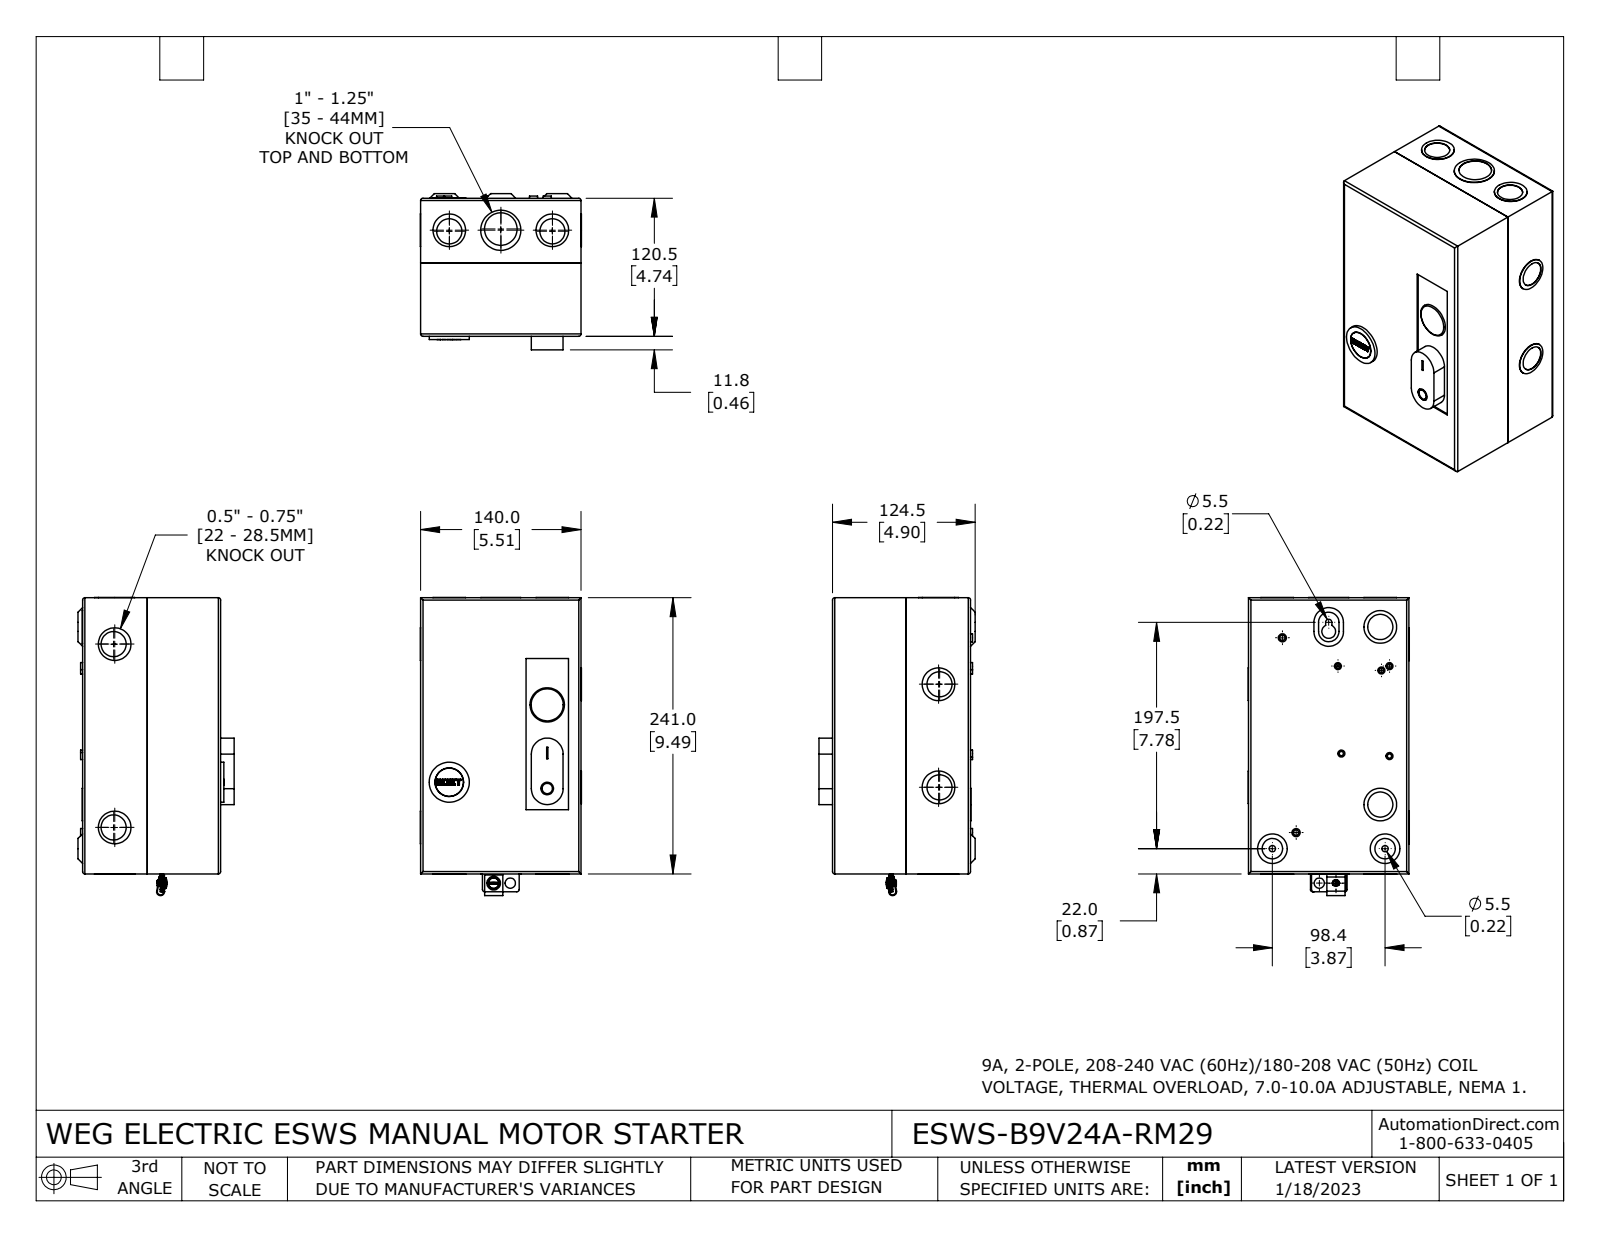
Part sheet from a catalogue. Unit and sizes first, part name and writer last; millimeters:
Units: millimetres
Overall size (bounding box): 260.3 × 140.6 × 136.3
Round holes (diameter × count): ⌀3.7 ×5, ⌀21.9 ×4, ⌀4.6 ×2, ⌀5.5 ×2, ⌀9 ×2, ⌀21.9 ×2, ⌀22 ×2, ⌀22.5 ×2, ⌀6.5 ×1, ⌀7.7 ×1, ⌀11 ×1, ⌀11.9 ×1
Round bosses / shafts (diameter × count): ⌀28.5 ×6, ⌀6.1 ×5, ⌀28.5 ×2, ⌀7.1 ×2, ⌀35.1 ×1, ⌀35 ×1, ⌀30.3 ×1, ⌀29.2 ×1
Partial cylindrical surfaces — rounded edges, fillets, slot ends (radius × count): R0.1 ×34, R2 ×13, R0.8 ×4, R2.7 ×3, R1.5 ×2, R1.9 ×2, R3.1 ×2, R3.5 ×2
Main face-to-face distances: 1.2, 119.3, 138.8, 118.1, 239.8, 120.5, 137.6, 140, 1.8, 1.6
Hole centre spacings: 14.5, 35, 45, 86, 90, 125, 152.3, 190.1
Volume: 266 000 mm³ · Surface area: 377 500 mm²
Bodies: 7 solids, 435 faces (168 planar, 230 cylindrical, 37 other)
Part name (STEP PRODUCT): ESWS-B9V24A-RM29
STEP written by: SolidWorks 2021 (CONFIG_CONTROL_DESIGN)
